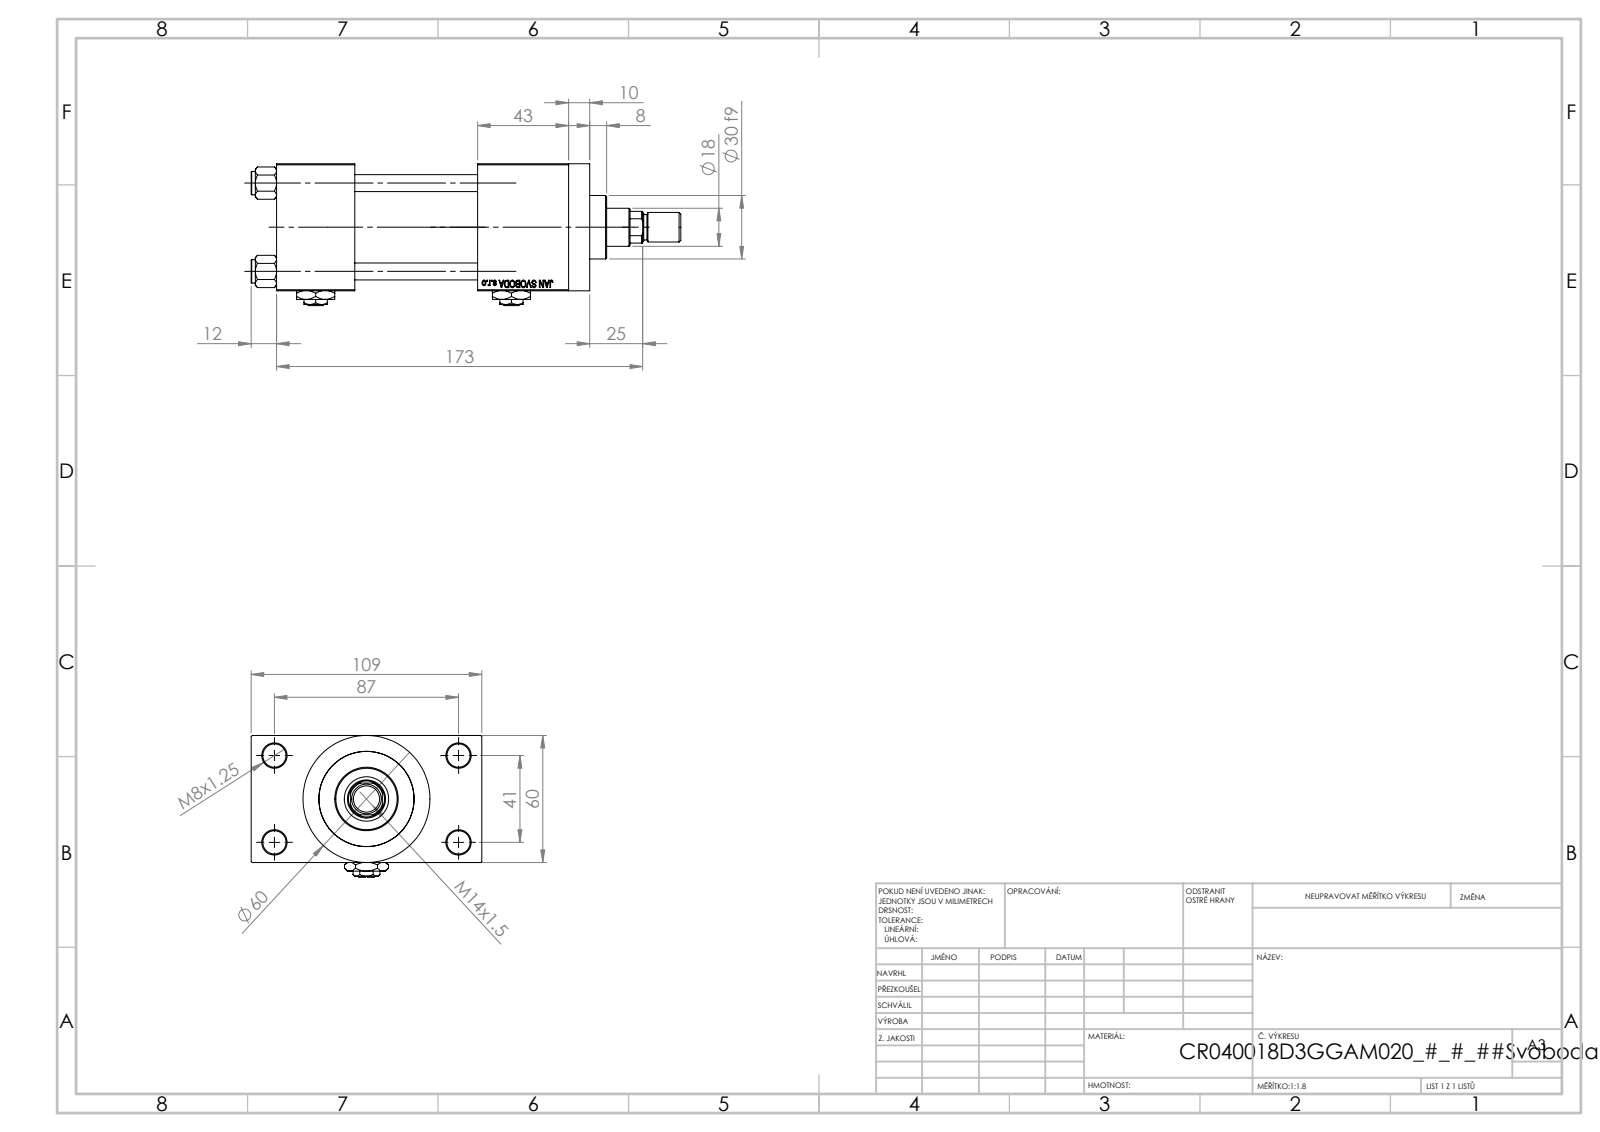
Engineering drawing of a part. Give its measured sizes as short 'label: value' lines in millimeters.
name: V215CR_D_TYCINKA; V215CR_VCP_D; NUT_M5_D; ROD_END_AH (+3 more)
written by: SolidWorks 2019 (CONFIG_CONTROL_DESIGN)
unit: mm
bodies: 14 solids, 1220 faces (550 planar, 104 cylindrical, 566 other)
size: 203 × 109 × 67
volume: 518 264 mm³; area: 125 041 mm²
holes: 4× ⌀8, 4× ⌀11, 2× ⌀7, 2× ⌀16.66, 2× ⌀24, 1× ⌀8.5, 1× ⌀18, 1× ⌀21, 1× ⌀31, 1× ⌀40, 1× ⌀45
bosses: 4× ⌀11, 1× ⌀60, 1× ⌀46, 1× ⌀30, 1× ⌀14, 1× ⌀12
rounds: 1× R8.5
face distances: 60, 24.5, 84.5, 58, 37, 95, 43, 138, 101, 109
hole spacings: 22.65, 29.49, 41.7, 47.15, 48.09, 64.35, 76.49, 41
